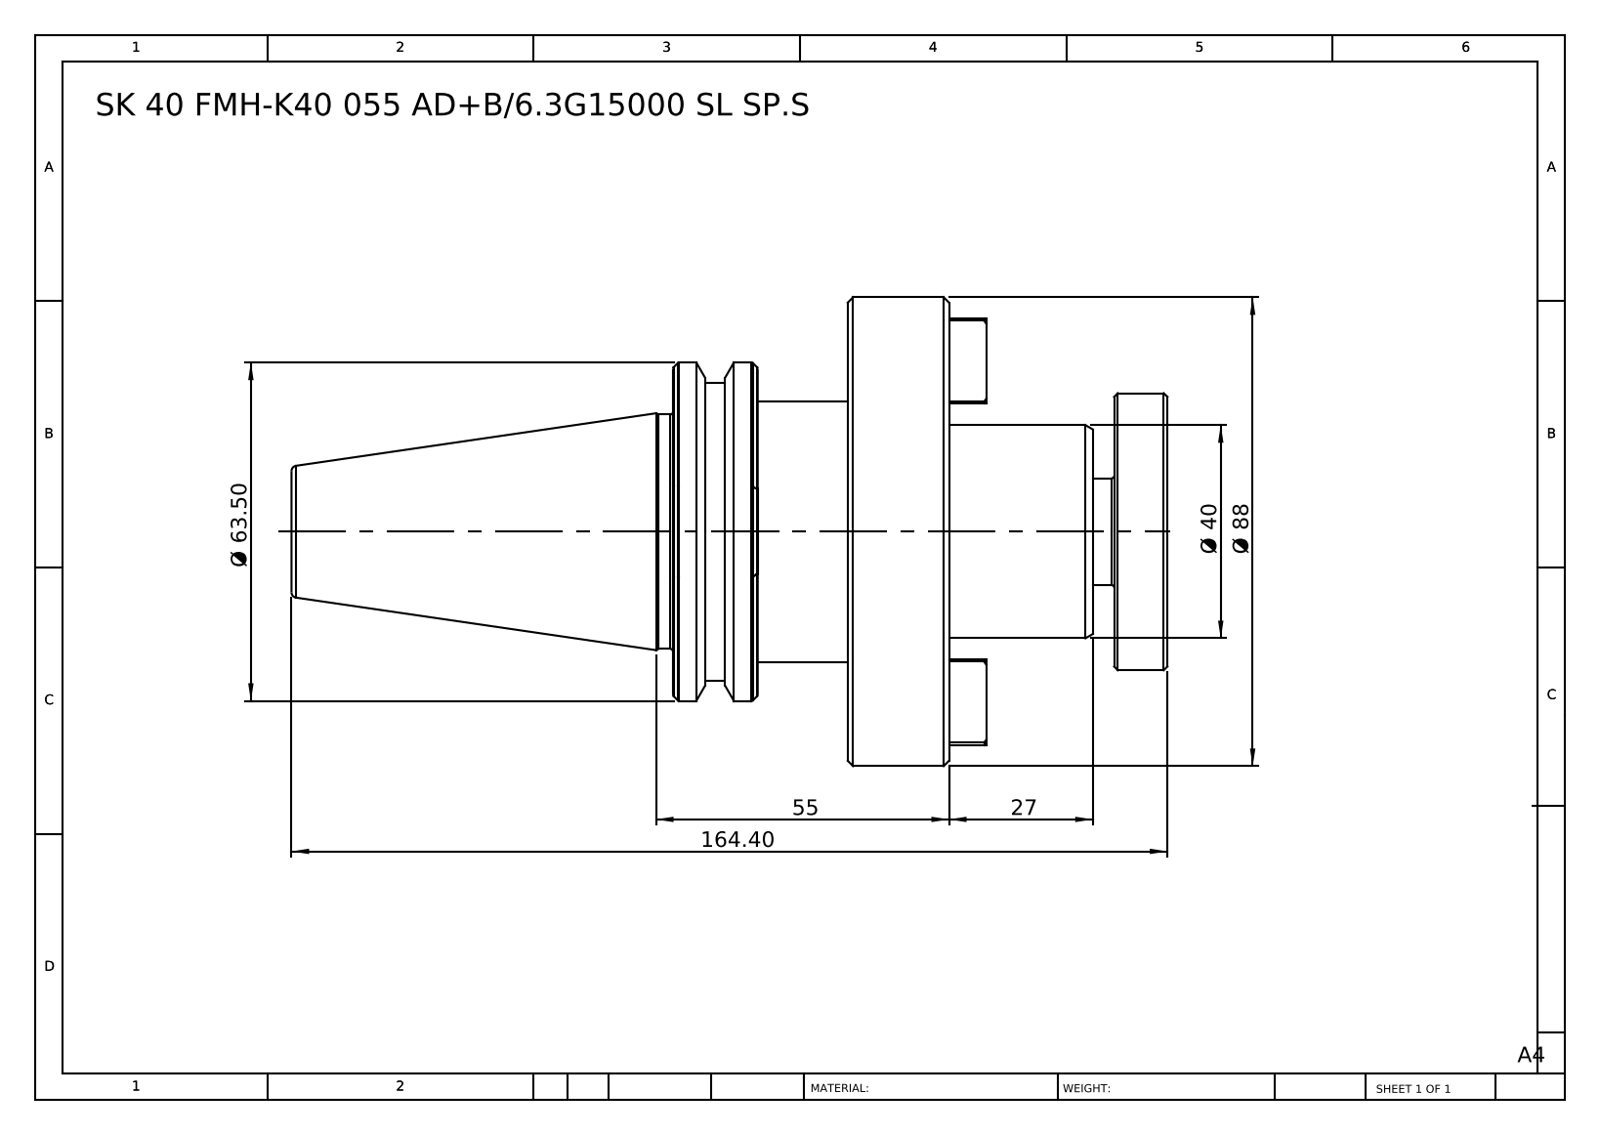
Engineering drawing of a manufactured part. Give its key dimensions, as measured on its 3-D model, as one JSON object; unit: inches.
{"part_name": "SK40 FMH40 055 AD-6.3G15000 SL SP.S", "step_written_by": "SolidWorks 2014 (CONFIG_CONTROL_DESIGN)", "units": "inches", "bodies": {"solids": 1, "faces": 115, "planar": 36, "cylindrical": 18, "other": 61}, "overall_size": [6.472, 3.465, 3.465], "volume_in3": 19.78, "surface_area_in2": 65.72, "round_bosses_or_shafts": [[3.465, 1], [2.5, 1], [2.205, 1], [2.047, 1], [1.929, 1], [1.732, 1], [1.575, 1], [0.787, 1]], "face_to_face_distances": [0.748, 1.614, 2.362, 0.394, 1.22, 1.969, 3.654, 3.26, 2.039, 1.291]}
